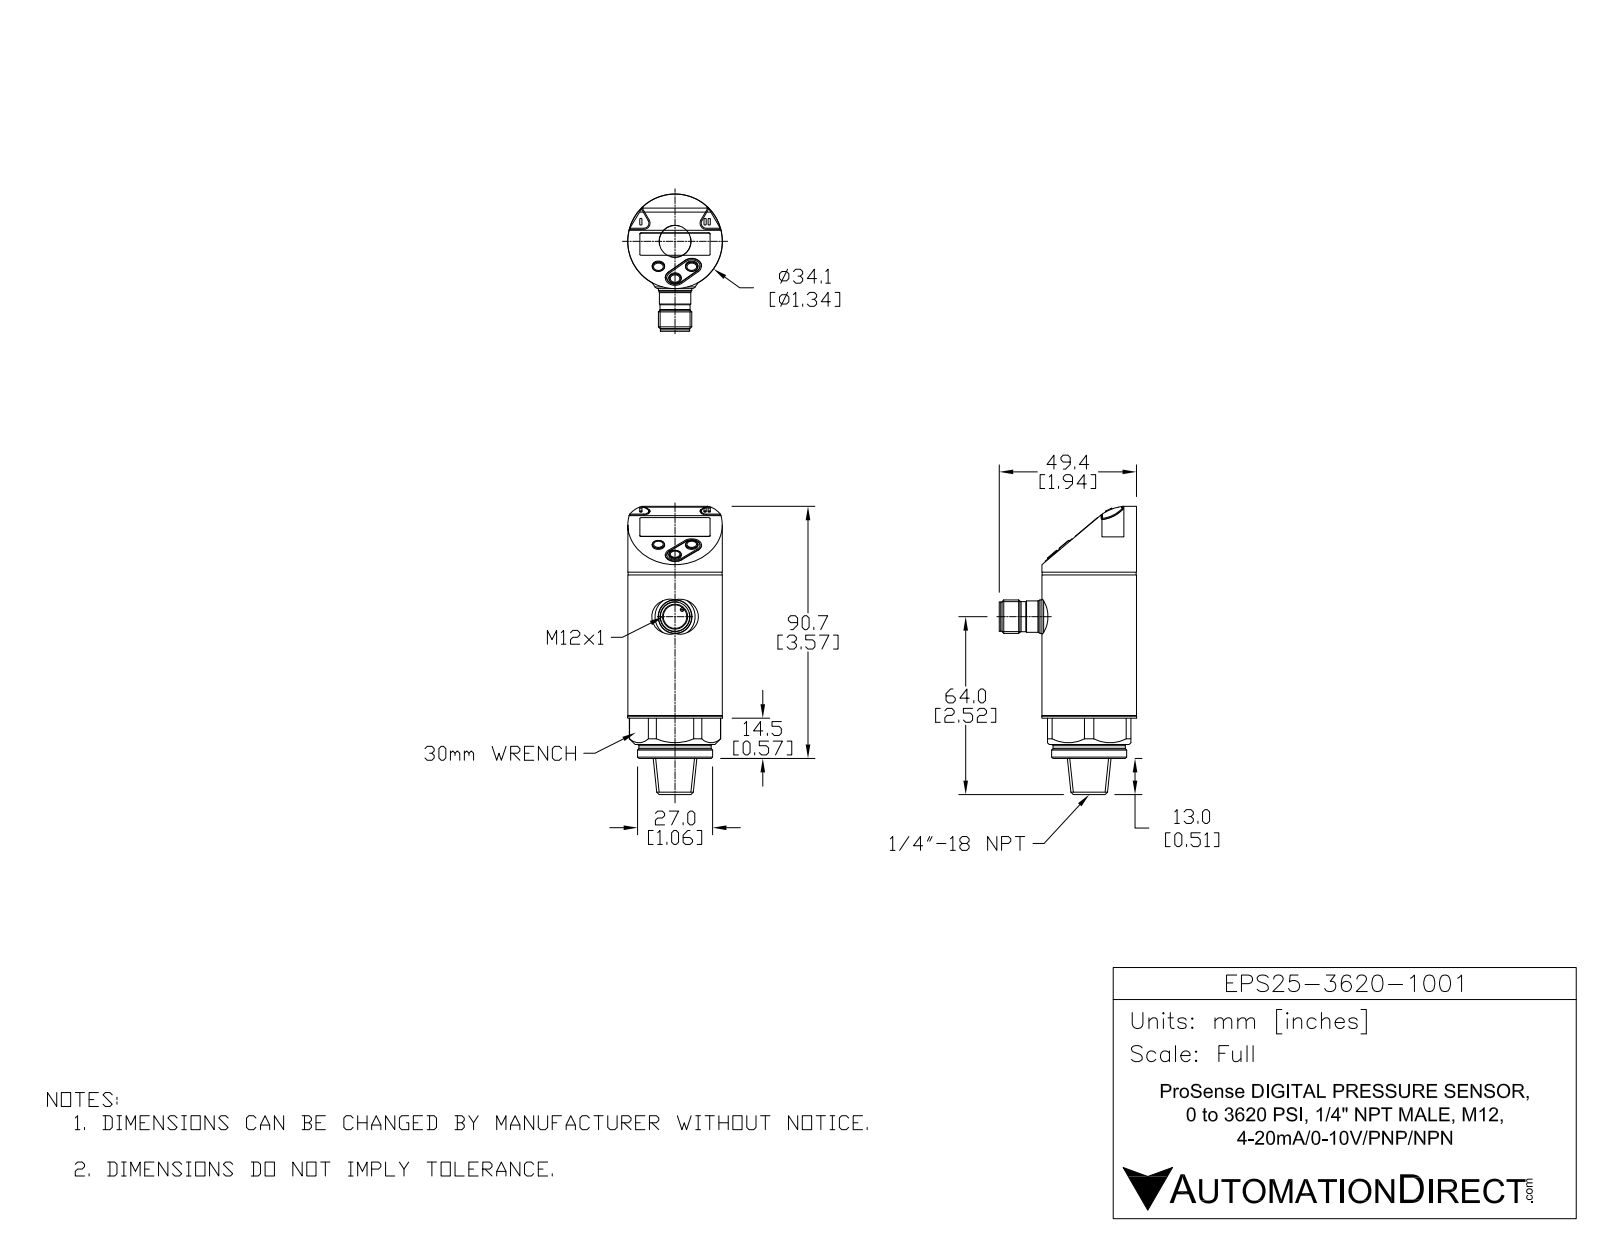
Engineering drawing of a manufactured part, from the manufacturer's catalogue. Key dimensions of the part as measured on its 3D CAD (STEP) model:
Part name (STEP PRODUCT): EPS25-3620-1001
STEP written by: SolidWorks 2016 (AUTOMOTIVE_DESIGN)
Units: millimetres
Bodies: 11 solids, 370 faces (207 planar, 84 cylindrical, 79 other)
Overall size (bounding box): 103.7 × 49.4 × 34.1
Volume: 72 203 mm³ · Surface area: 21 365 mm²
Round holes (diameter × count): ⌀4.2 ×1, ⌀8.45 ×1
Round bosses / shafts (diameter × count): ⌀1.4 ×4, ⌀1 ×4, ⌀34.1 ×1, ⌀34 ×1, ⌀33.8 ×1, ⌀27 ×1, ⌀26 ×1, ⌀12 ×1
Partial cylindrical surfaces — rounded edges, fillets, slot ends (radius × count): R1.8 ×2, R2.2 ×2, R3 ×2, R3.5 ×2, R15 ×2, R0.61 ×1, R6.8 ×1, R16.44 ×1
Main face-to-face distances: 0.68, 11.5, 12.18, 10.68, 1.5, 10, 2, 2.5, 14, 4
